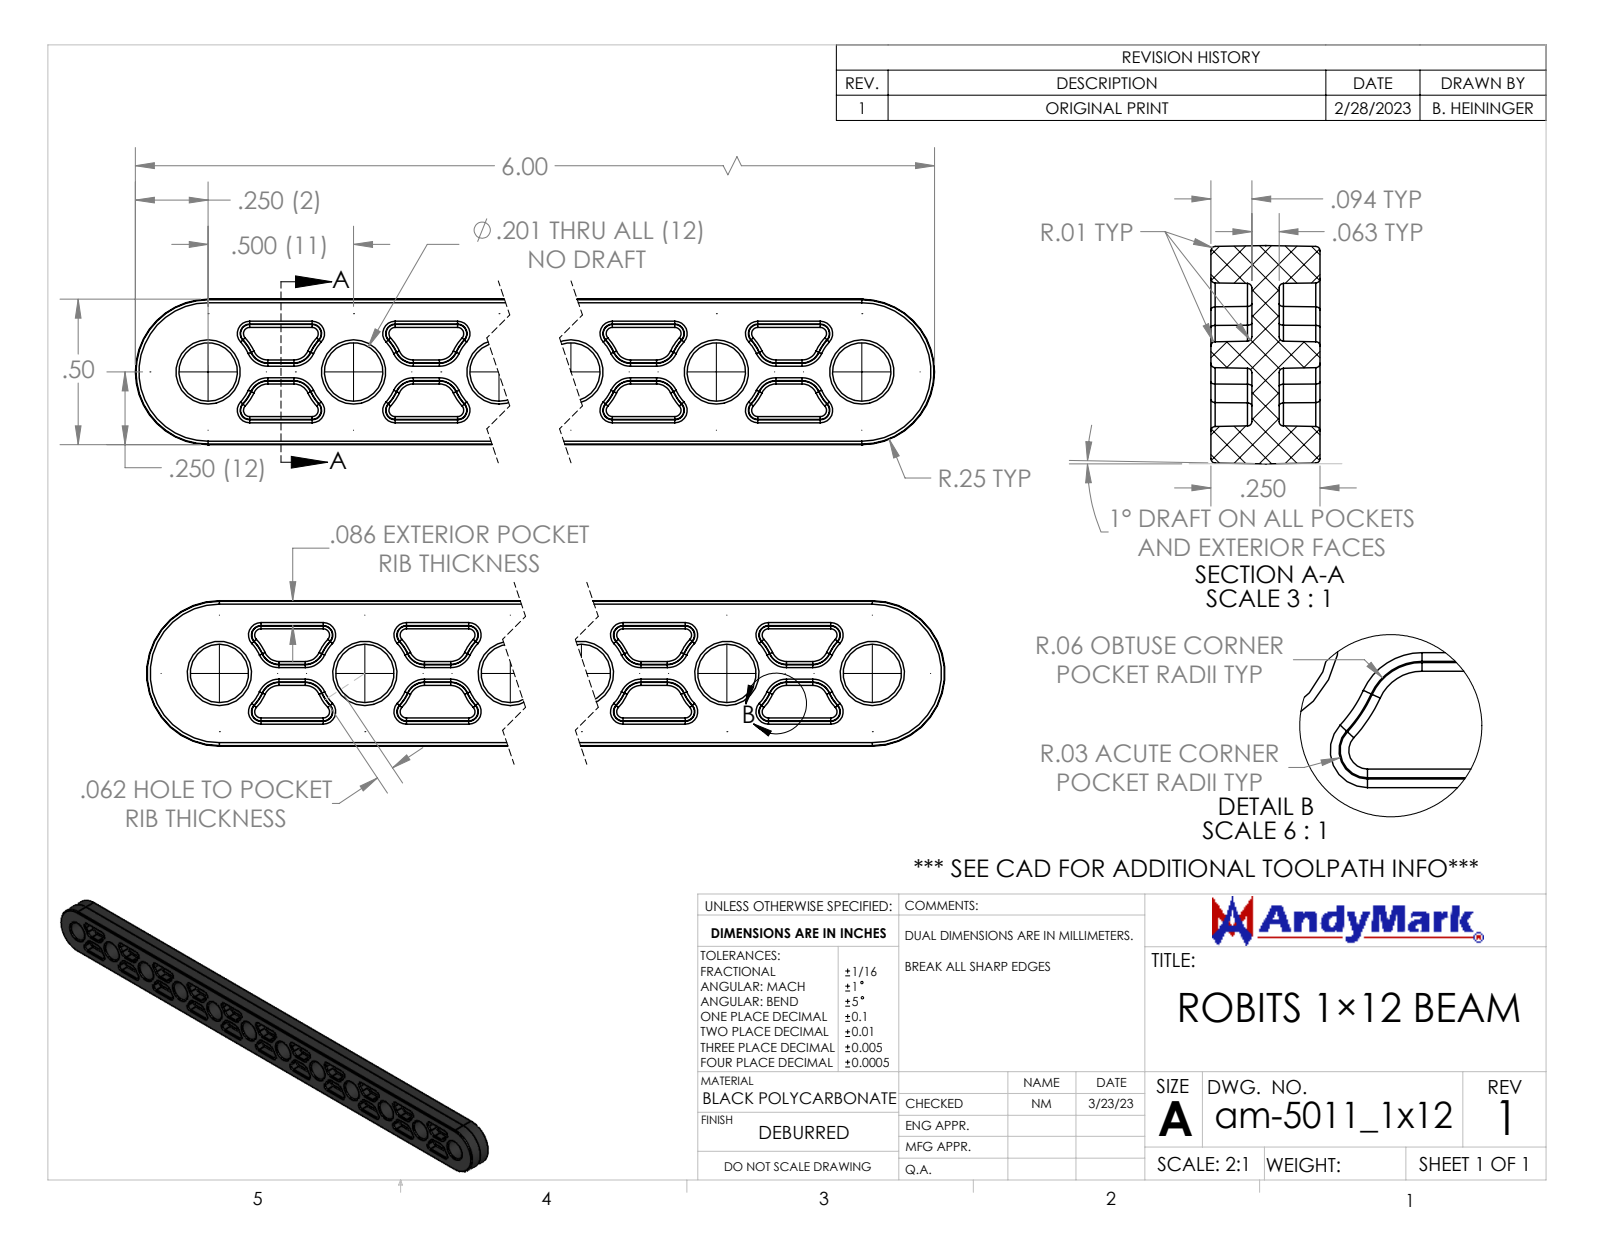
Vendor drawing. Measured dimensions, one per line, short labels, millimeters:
name: am-5011_1x12 RoBits 1×12 Beam
written by: SolidWorks 2022 (AUTOMOTIVE_DESIGN)
unit: mm
bodies: 1 solid, 1194 faces (138 planar, 207 cylindrical, 849 other)
size: 152.4 × 12.7 × 6.4
volume: 8 370 mm³; area: 8 084 mm²
holes: 12× ⌀5.1
rounds: 22× R0.3, 1× R4.1
face distances: 6.4, 12.7, 2.4, 4, 2.2, 10.5, 1.6, 8.3, 5.5, 7.2
hole spacings: 12.7, 25.4, 38.1, 50.8, 63.5, 76.2, 88.9, 101.6
